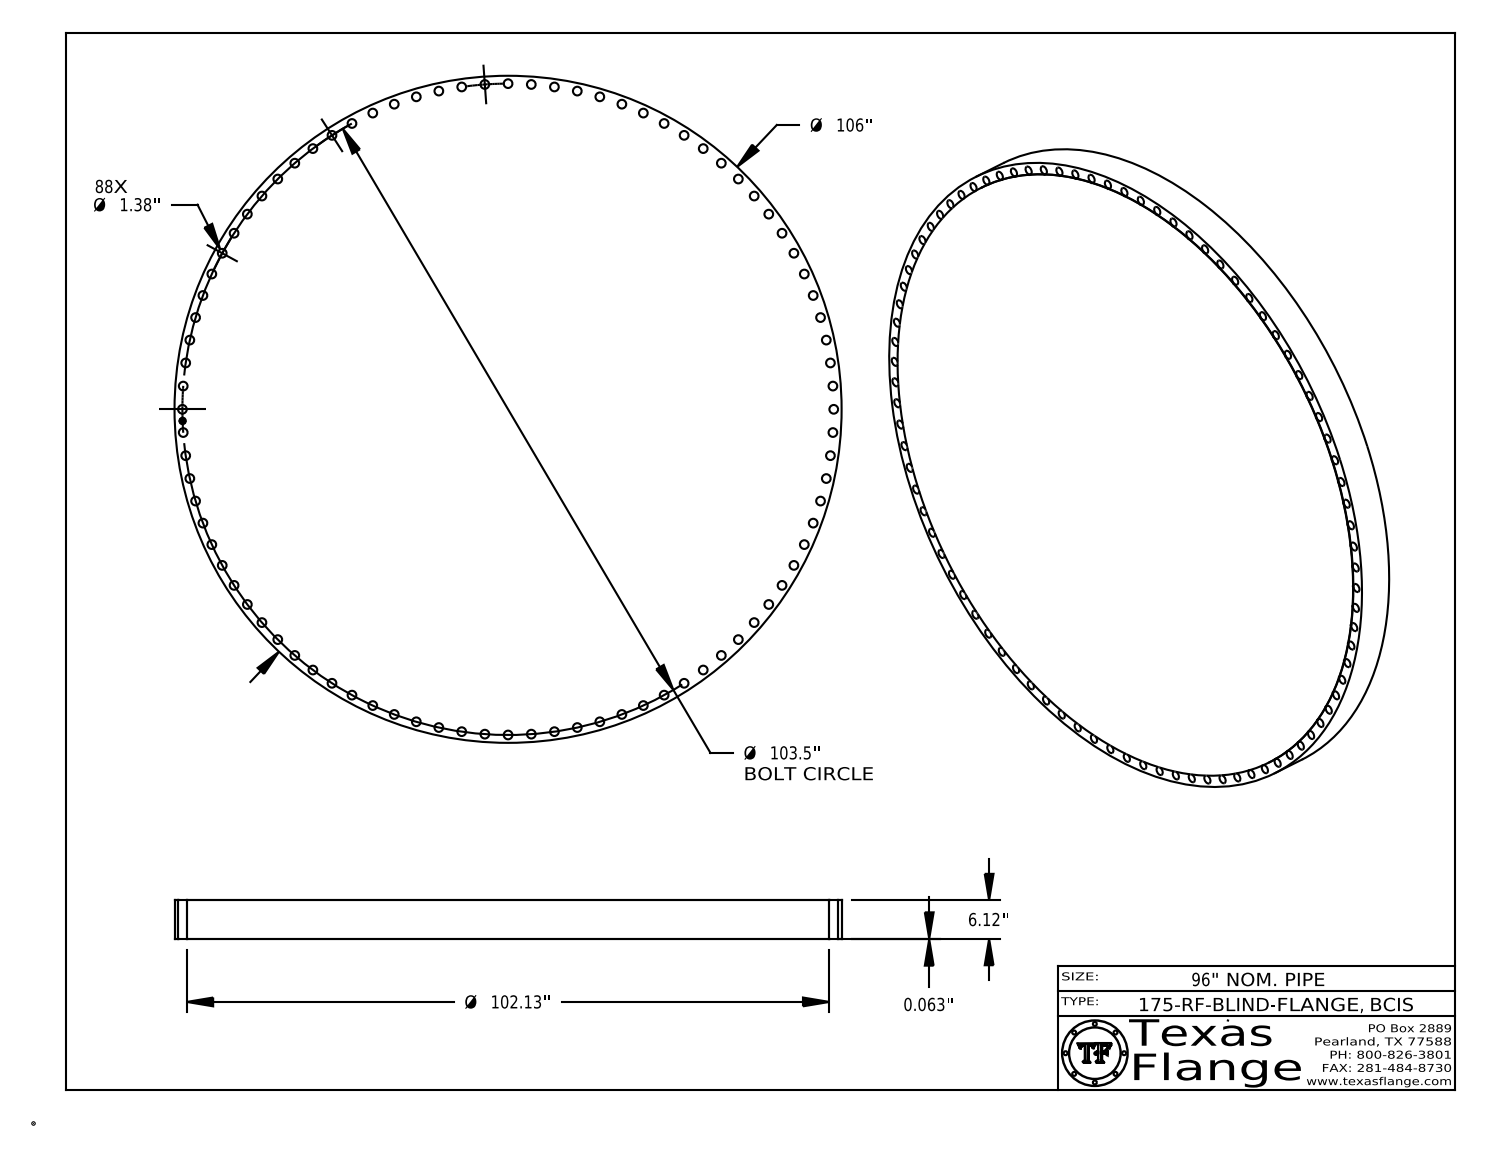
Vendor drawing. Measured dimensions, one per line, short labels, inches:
name: 175-RF-BLIND, Series BCIS
written by: CATIA V5 STEP AP214 (AUTOMOTIVE_DESIGN)
unit: in
bodies: 1 solid, 654 faces (368 planar, 286 cylindrical, 0 other)
size: 106 × 106 × 6.183
volume: 53 714 in³; area: 21 779 in²
holes: 88× ⌀1.38, 1× ⌀1
bosses: 8× ⌀0.061, 1× ⌀106, 1× ⌀102.13, 1× ⌀0.788
face distances: 6.183, 0.063, 6.12, 0.015, 6.168, 6.105, 0.298, 0.292, 0.054, 0.193
hole spacings: 3.694, 22, 18.377, 32.685, 7.383, 11.064, 96.974, 98.204
